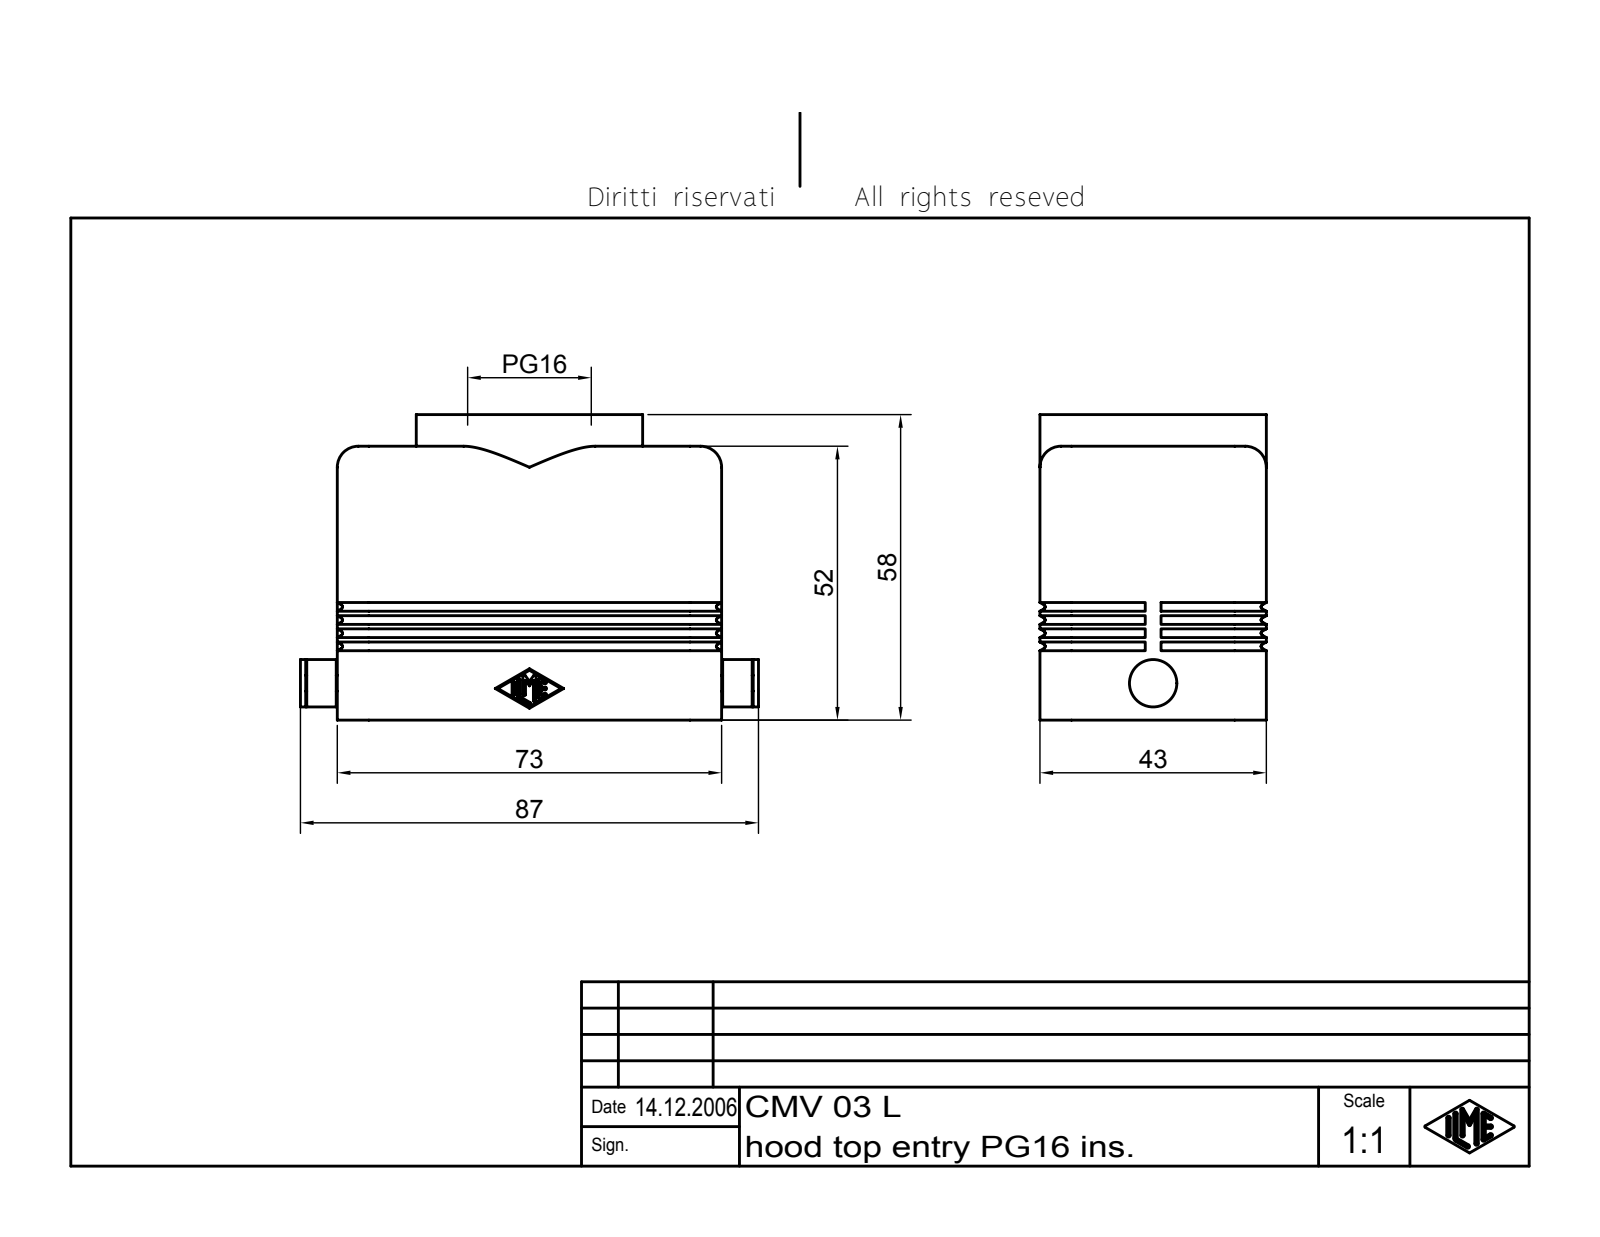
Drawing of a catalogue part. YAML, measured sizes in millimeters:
part_name: "CMV 03 L"
step_written_by: "Autodesk Inventor 7 (AUTOMOTIVE_DESIGN)"
units: millimeters
bodies: {solids: 1, faces: 479, planar: 119, cylindrical: 200, other: 160}
overall_size: [87, 58, 43]
volume: 56477
surface_area: 30323
round_holes:
  - {diameter: 19.38, count: 1}
  - {diameter: 21.16, count: 1}
round_bosses_or_shafts:
  - {diameter: 43, count: 1}
  - {diameter: 9, count: 1}
  - {diameter: 3, count: 1}
partial_cylinders:
  - {radius: 0.4, count: 32}
  - {radius: 0.25, count: 14}
  - {radius: 1.5, count: 4}
  - {radius: 3, count: 4}
  - {radius: 4, count: 4}
  - {radius: 6, count: 4}
  - {radius: 5, count: 2}
face_to_face_distances: [3, 40, 43, 37, 11.5, 8.5, 70, 9, 73, 31.5]
